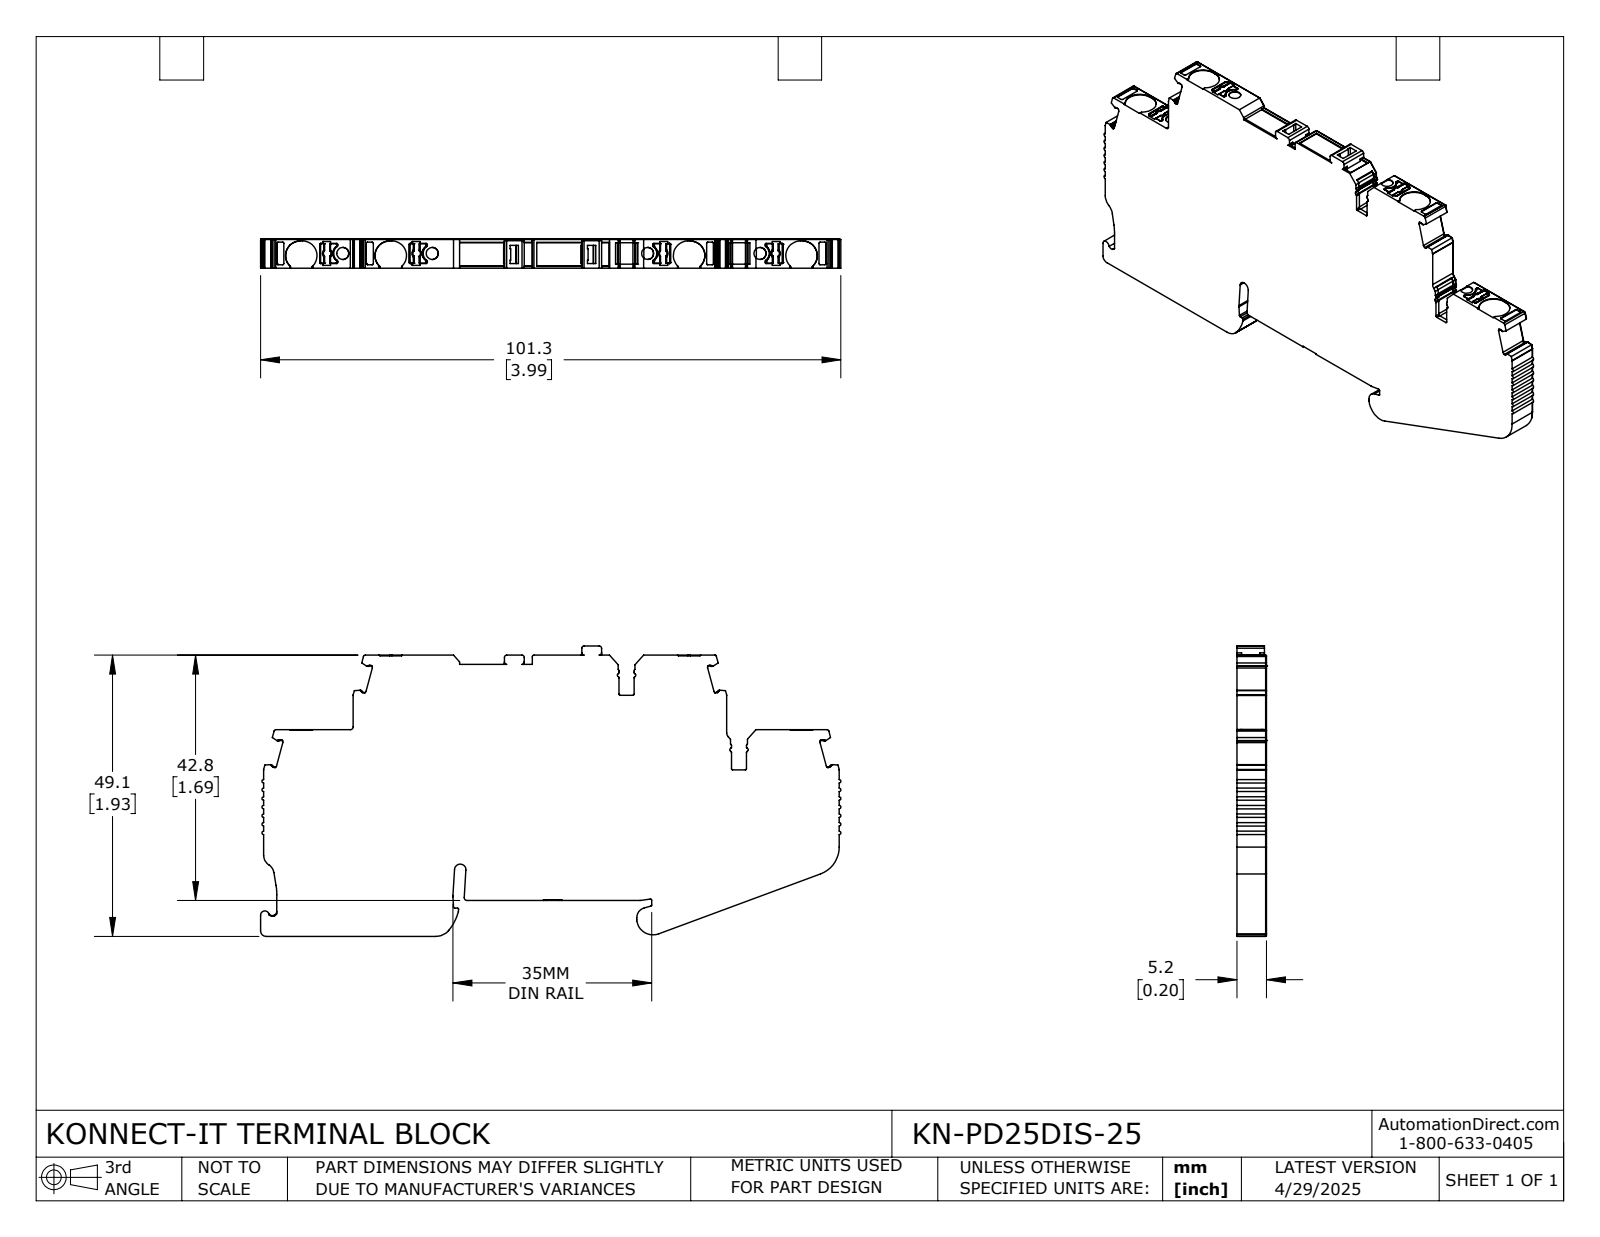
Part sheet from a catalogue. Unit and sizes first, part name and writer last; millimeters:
Units: millimetres
Overall size (bounding box): 101.34 × 50.69 × 5.15
Round holes (diameter × count): ⌀2.1 ×4
Partial cylindrical surfaces — rounded edges, fillets, slot ends (radius × count): R0.2 ×85, R0.3 ×38, R0.1 ×25, R0.15 ×16, R0.4 ×13, R0.5 ×13, R0.6 ×9, R0.15 ×8
Main face-to-face distances: 5.15, 6.27, 13.01, 42.71, 48.98, 49.09, 42.82, 13.12, 29.7, 35.97
Hole centre spacings: 15.62, 19.63, 37.61, 53.23, 57.24, 72.86
Volume: 20 143 mm³ · Surface area: 9 818 mm²
Bodies: 1 solid, 883 faces (454 planar, 386 cylindrical, 43 other)
Part name (STEP PRODUCT): KN-PD25DIS-25
STEP written by: SolidWorks 2024 (CONFIG_CONTROL_DESIGN)
